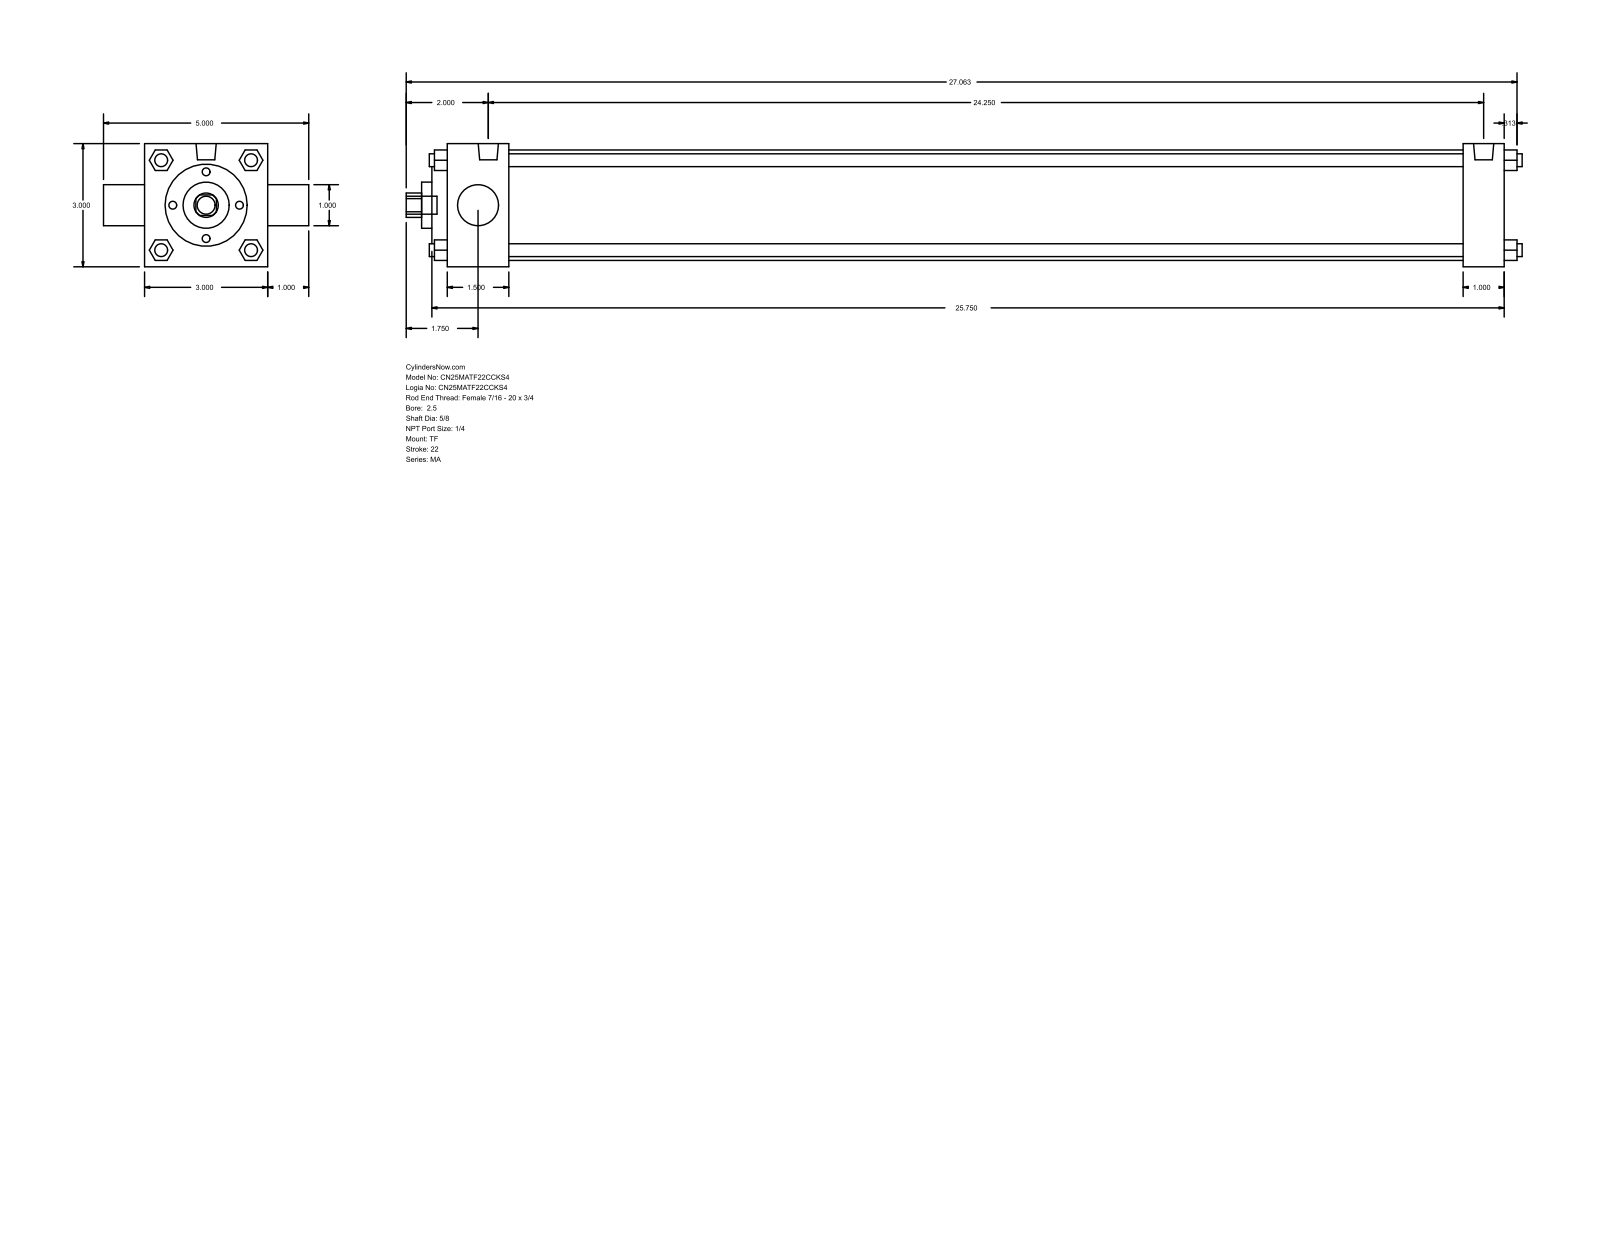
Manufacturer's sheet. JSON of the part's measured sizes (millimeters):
{"part_name": "MA_TF__0250_0.625", "step_written_by": "GSSL Pune (CONFIG_CONTROL_DESIGN)", "units": "millimeters", "bodies": {"solids": 0, "faces": 122, "planar": 93, "cylindrical": 29, "other": 0}, "overall_size": [690.56, 127, 76.2], "round_holes": [[15.88, 1], [25.4, 1], [28.57, 1], [50.8, 1], [68.33, 1]], "round_bosses_or_shafts": [[7.94, 7], [12.49, 2], [11.11, 1]], "partial_cylinders_radius": [[7.54, 1]], "face_to_face_distances": [76.2, 654.05, 25.4, 38.1, 628.65, 590.55, 615.95, 12.7, 9.52, 47.62]}
